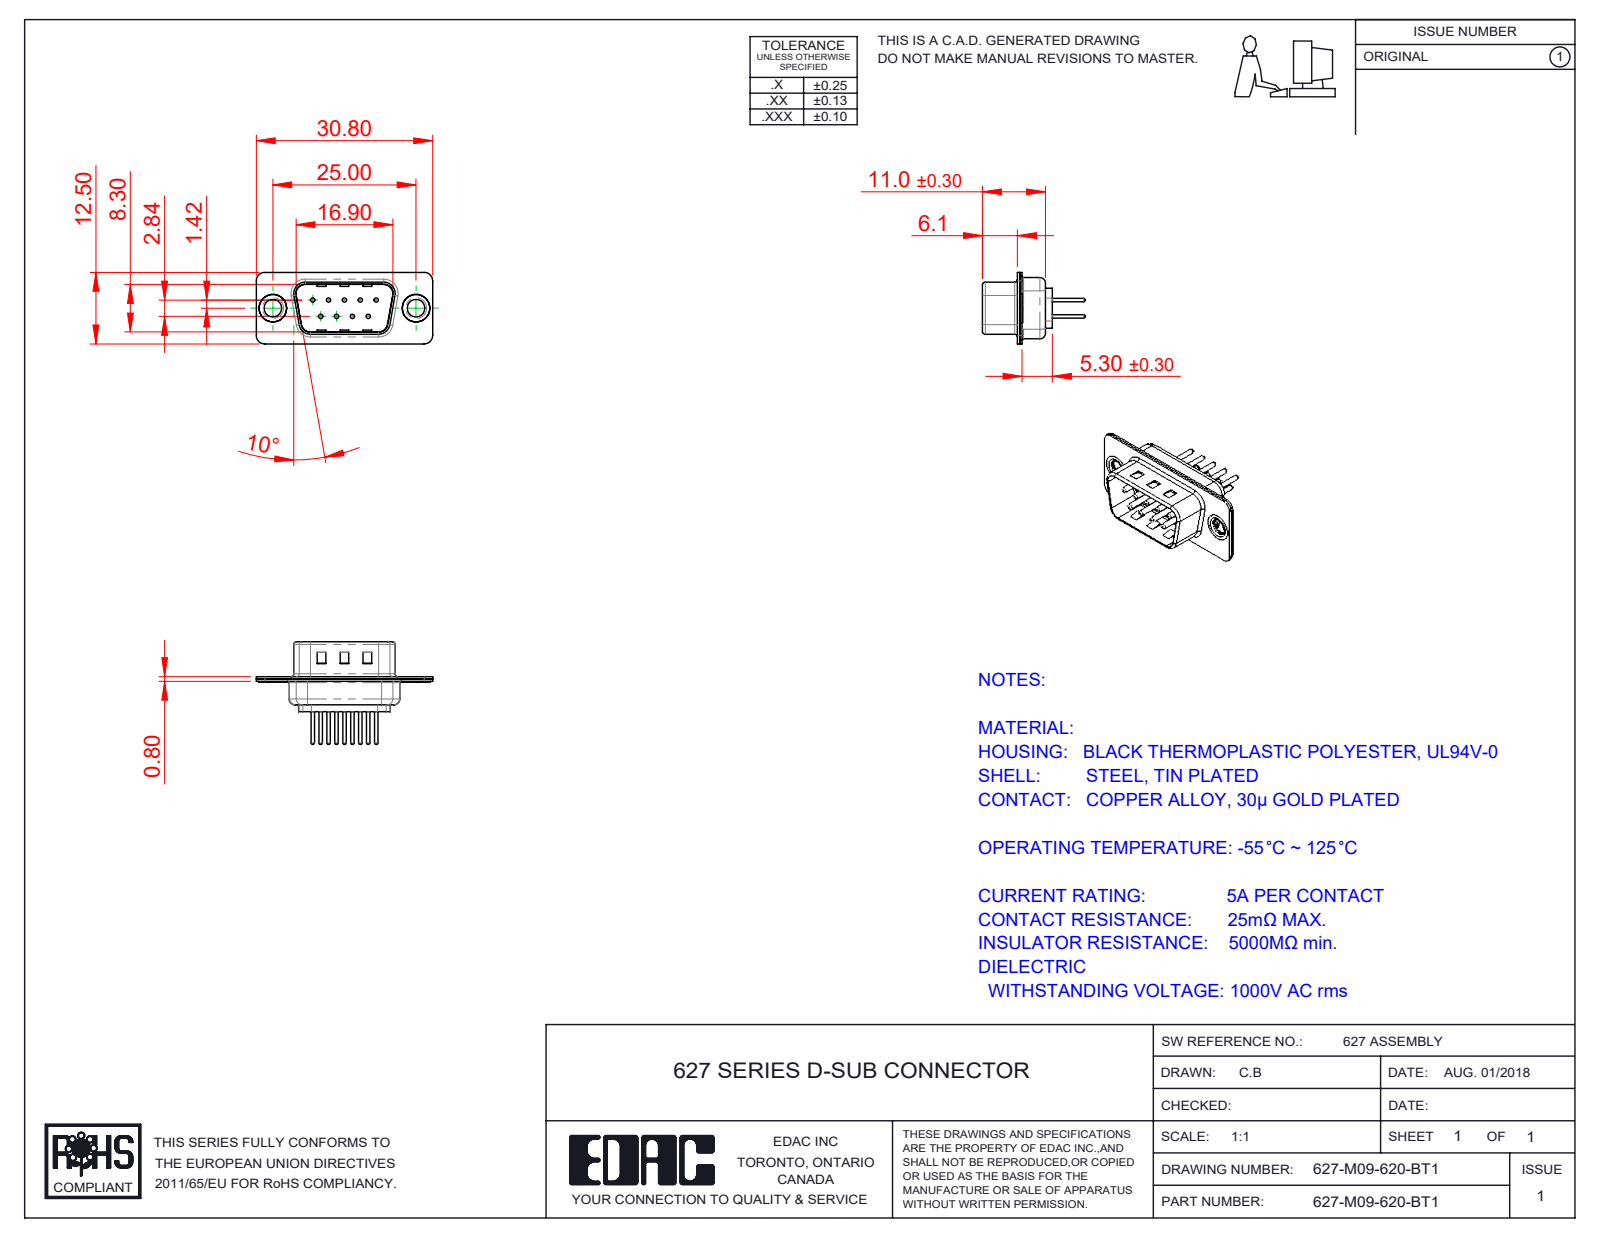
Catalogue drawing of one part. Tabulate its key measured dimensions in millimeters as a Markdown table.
| quantity | value |
| --- | --- |
| part name | 627M Shell Front_09 Contacts; 627M Thru Hole Rivet; 627M Shell Rear_09 Contacts; 627M Contact Row 2_20 (+3 more) |
| STEP written by | SolidWorks 2020 (CONFIG_CONTROL_DESIGN) |
| units | millimeters |
| bodies | 14 solids, 611 faces (170 planar, 239 cylindrical, 202 other) |
| overall size | 30.8 × 17.9 × 12.5 |
| volume | 1 232 mm³ |
| surface area | 3 429 mm² |
| round holes (diameter × count) | 0.75 × 9, 1.6 × 9, 2 × 9, 3.05 × 2, 4 × 2, 4.8 × 2 |
| round bosses / shafts (diameter × count) | 1.5 × 9, 0.6 × 9, 5 × 2, 4.9 × 2, 3.55 × 2 |
| partial cylindrical surfaces (radius × count) | 1.5 × 16, 2 × 12, 0.5 × 8, 1.6 × 8, 0.25 × 4, 0.6 × 4, 0.65 × 4, 0.9 × 4 |
| main face-to-face distances | 0.4, 0.8, 9.5, 9.1, 8.7, 0.65, 9.9, 1.2, 6.1, 5.7 |
| hole center spacings | 3.16, 2.77, 5.54, 5.03, 5.04, 8.31, 7.1, 7.48 |
